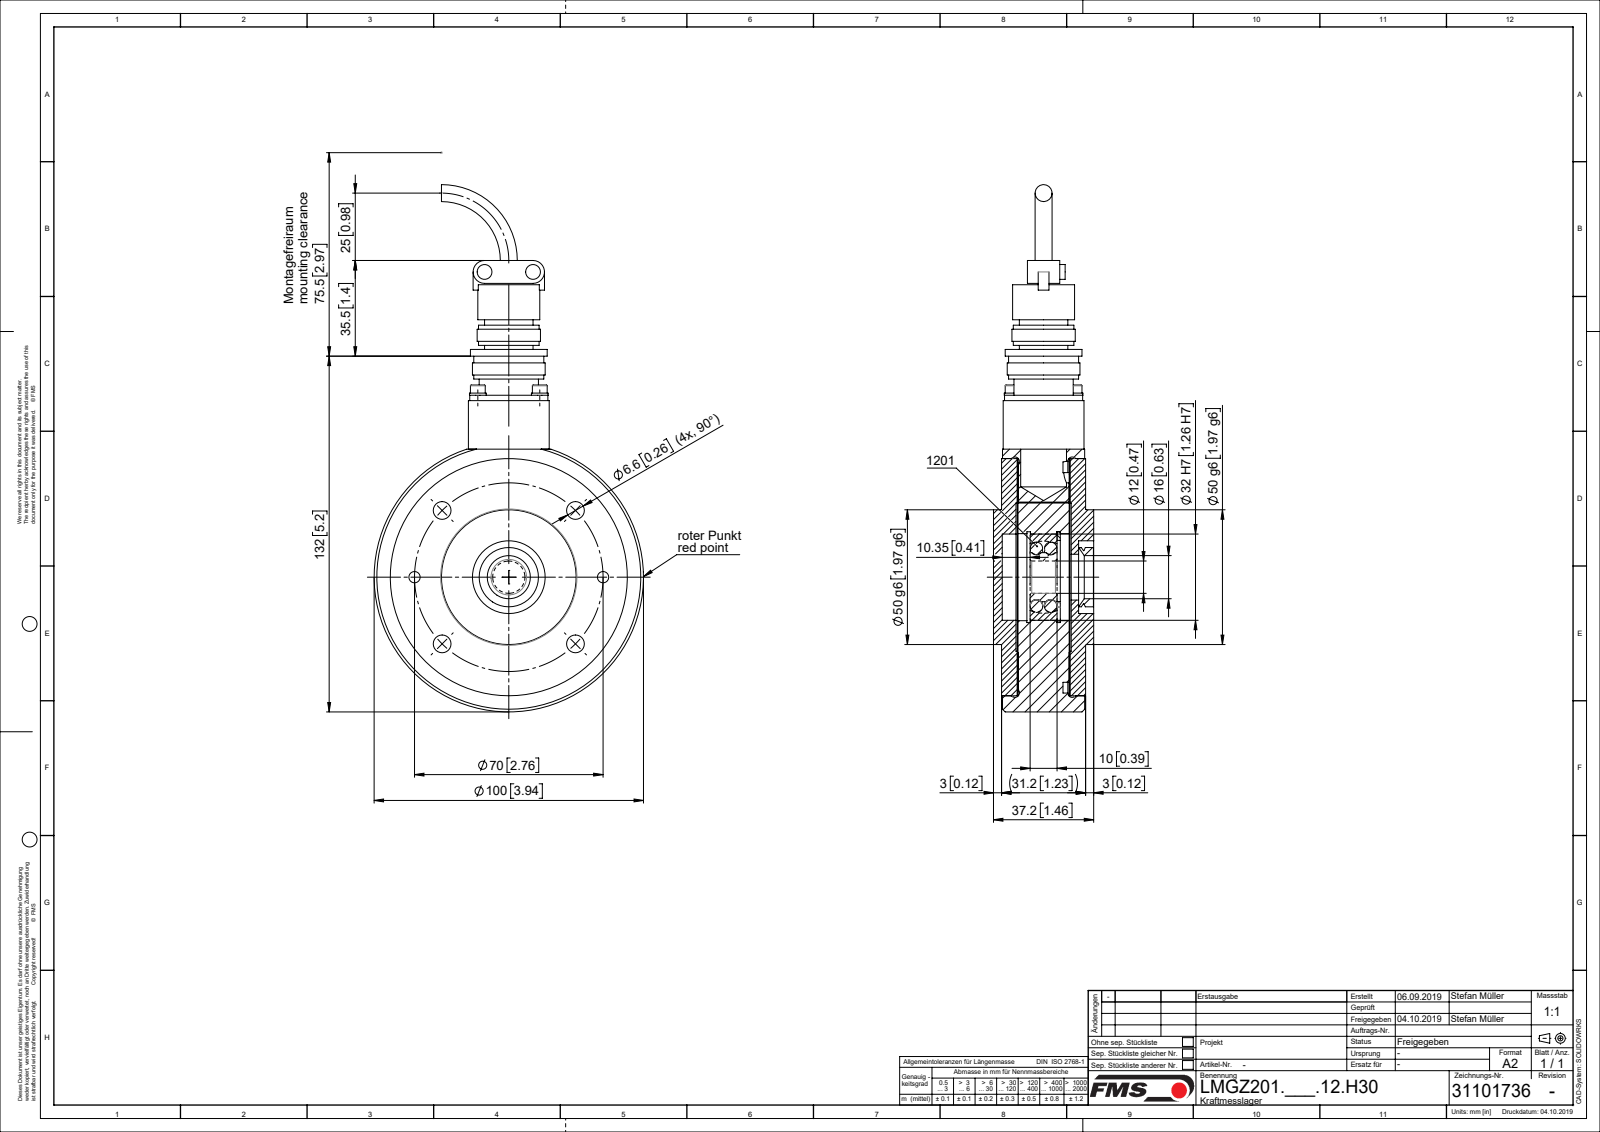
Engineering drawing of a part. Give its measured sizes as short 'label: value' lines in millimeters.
name: L50004; L4866604; TEIL1; L48891 (+8 more)
written by: Mechanical Desktop 2007 (CONFIG_CONTROL_DESIGN)
unit: mm
bodies: 20 solids, 379 faces (114 planar, 223 cylindrical, 42 other)
size: 195.65 × 100 × 37.2
volume: 265 032 mm³; area: 96 535 mm²
holes: 4× ⌀2.6, 4× ⌀3.2, 4× ⌀3.4, 4× ⌀6.6, 2× ⌀4, 2× ⌀5.5, 2× ⌀10, 1× ⌀12, 1× ⌀16, 1× ⌀17, 1× ⌀23, 1× ⌀25.4
bosses: 6× ⌀5.5, 4× ⌀6.2, 4× ⌀3, 4× ⌀2.5, 2× ⌀22, 2× ⌀8, 2× ⌀5, 1× ⌀100
rounds: 2× R4.25
face distances: 19.25, 19, 5.85, 25.1, 6.1, 25.35, 19.5, 5.5, 24.75, 20
hole spacings: 35, 16.26, 23, 26.79, 49.5, 64.67, 70, 32.53
